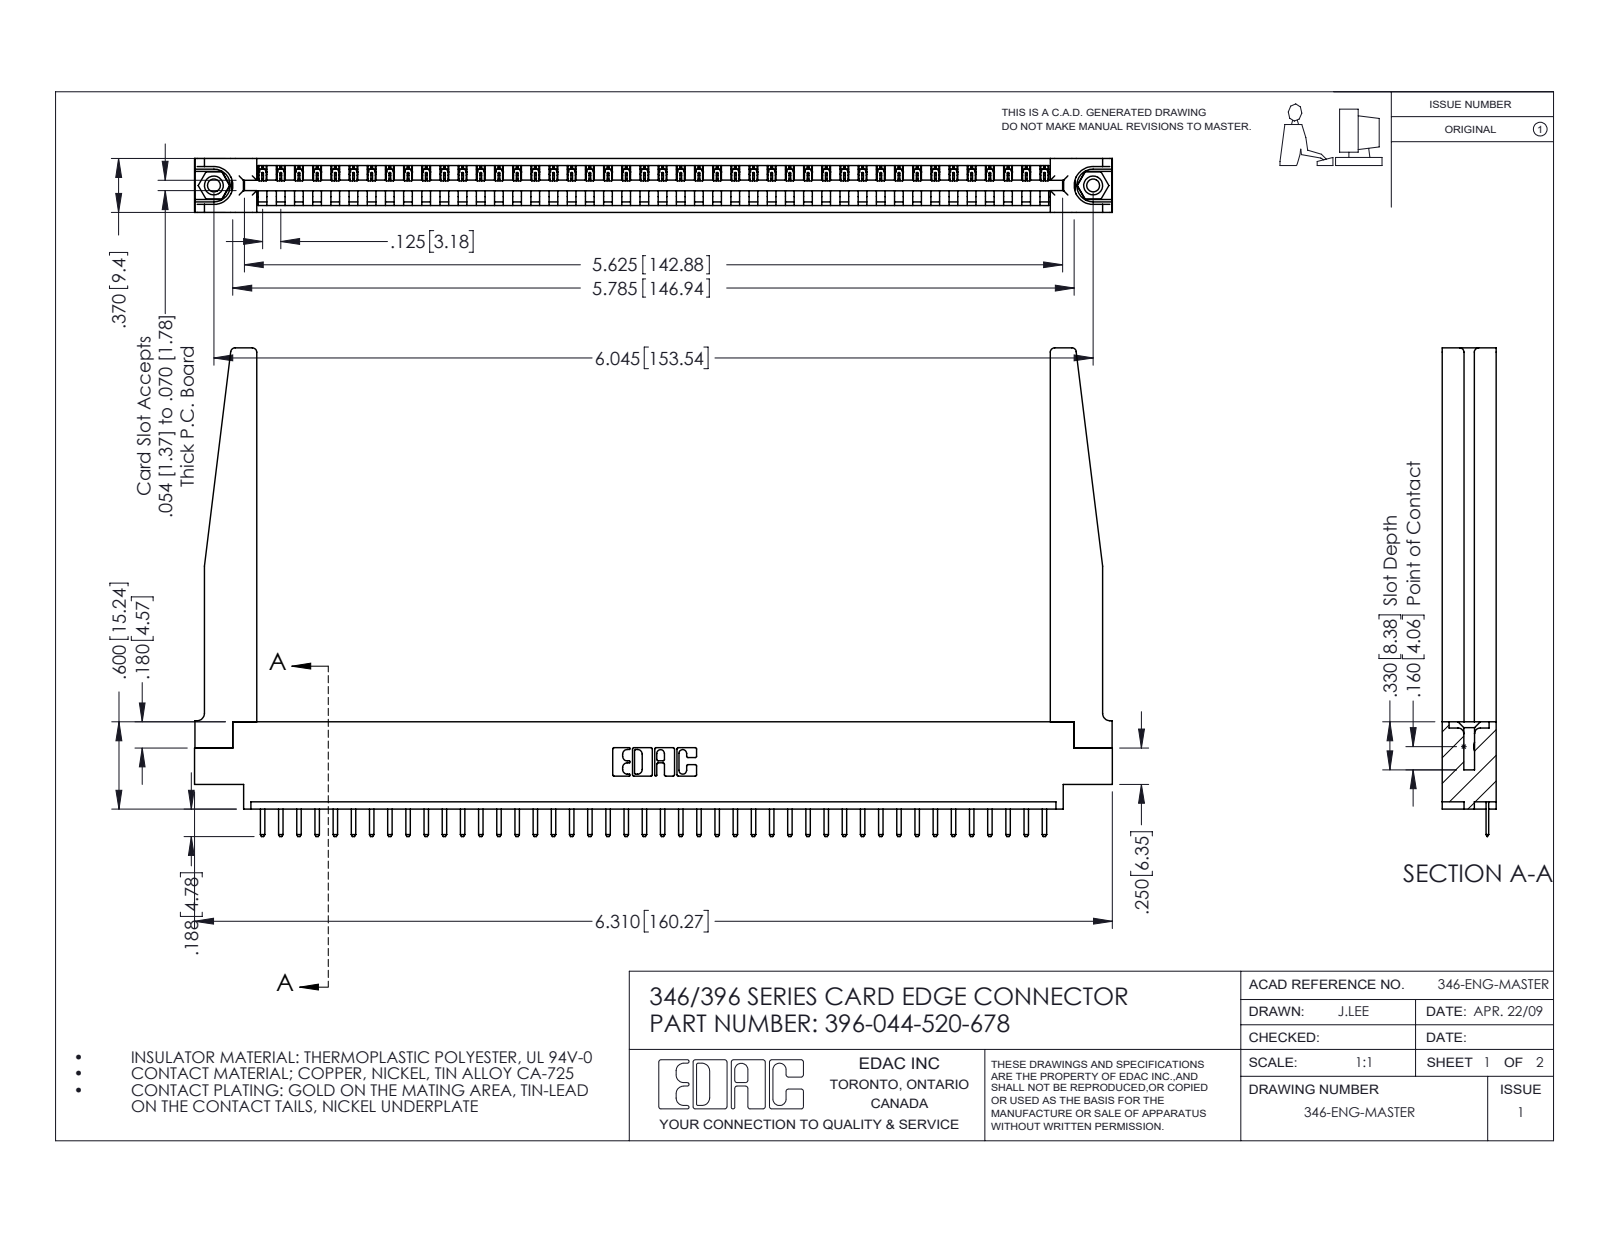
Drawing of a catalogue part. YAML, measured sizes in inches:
part_name: "346-220-078_345-220-078; 345-250-001_345-250-001-102; 346 Part_0.170 Offset - 0.156 Dia-TH; 345-292-001_345-293-120 (+1 more)"
step_written_by: "SolidWorks 2016 (CONFIG_CONTROL_DESIGN)"
units: inches
bodies: {solids: 49, faces: 3088, planar: 2070, cylindrical: 966, other: 52}
overall_size: [6.31, 3.358, 0.37]
volume: 1.341
surface_area: 38.97
round_holes:
  - {diameter: 0.089, count: 2}
  - {diameter: 0.125, count: 2}
  - {diameter: 0.156, count: 2}
  - {diameter: 0.064, count: 1}
round_bosses_or_shafts:
  - {diameter: 0.155, count: 2}
partial_cylinders:
  - {radius: 0.01, count: 90}
  - {radius: 0.006, count: 88}
  - {radius: 0.01, count: 22}
  - {radius: 0.03, count: 8}
  - {radius: 0.007, count: 6}
  - {radius: 0.031, count: 6}
  - {radius: 0.026, count: 3}
  - {radius: 0.031, count: 2}
face_to_face_distances: [0.37, 0.048, 0.322, 0.148, 0.072, 0.15, 0.25, 0.222, 0.1, 0.174]
hole_center_spacings: [0.246, 5.836, 6.045]
